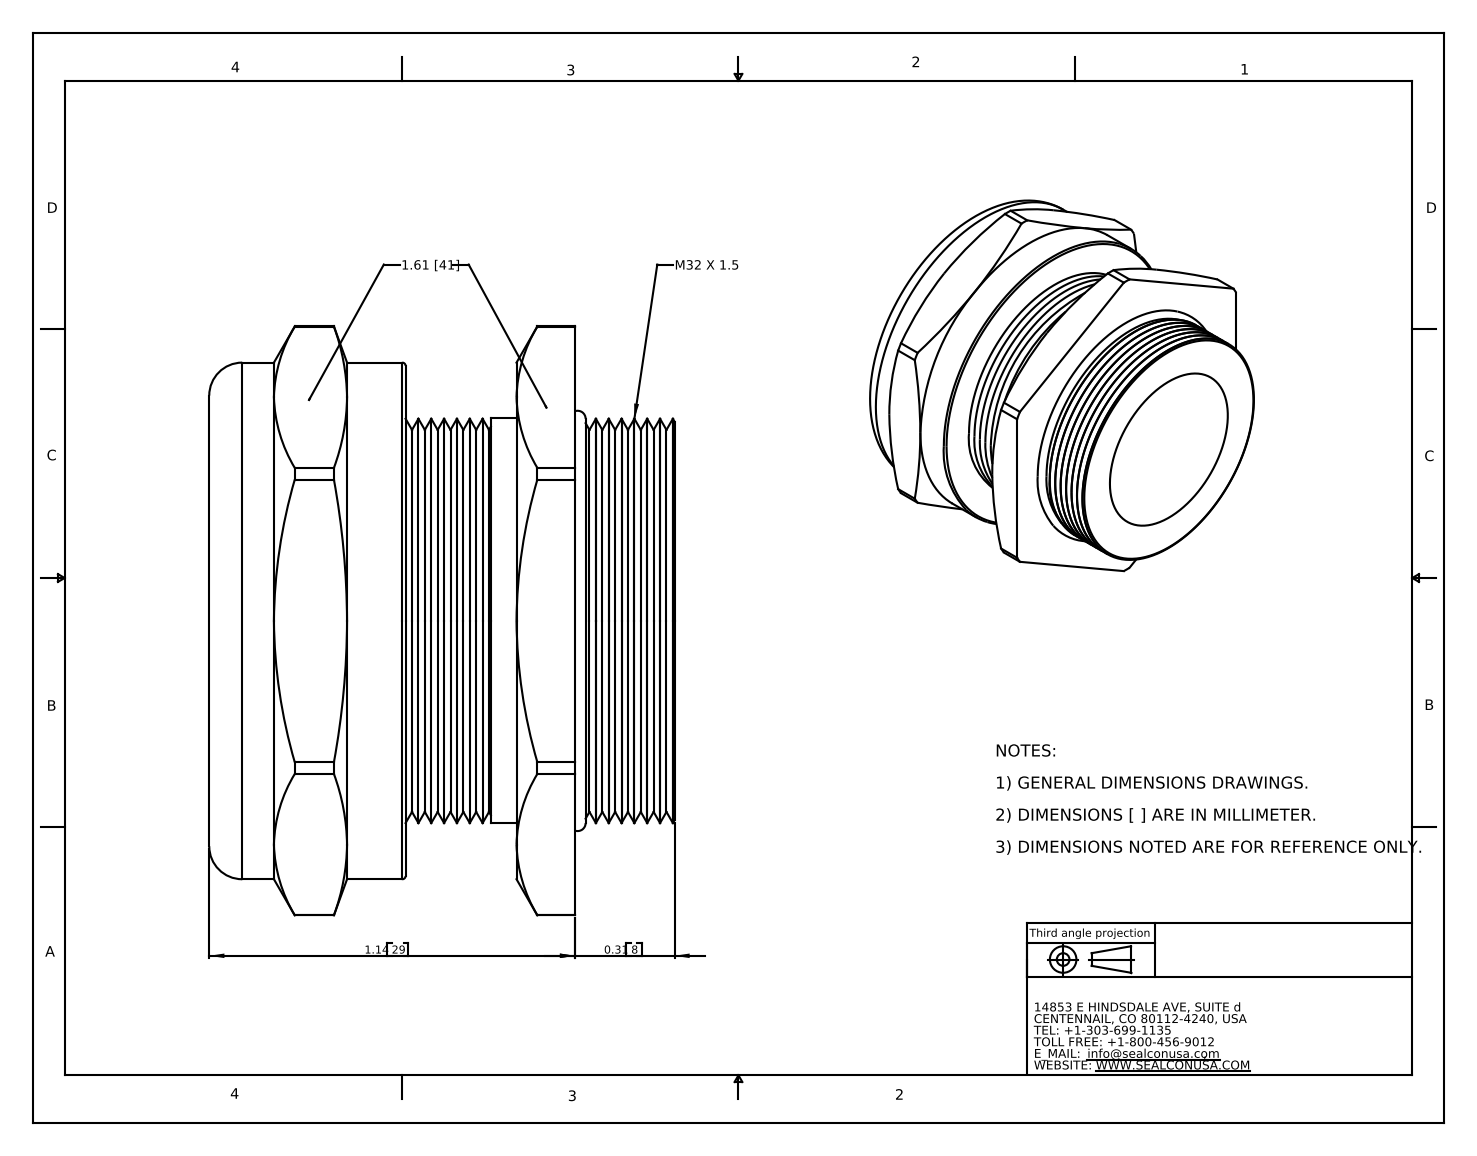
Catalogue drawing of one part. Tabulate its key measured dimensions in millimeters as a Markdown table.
| quantity | value |
| --- | --- |
| part name | CD32MR-SS |
| STEP written by | SolidWorks 2007 (CONFIG_CONTROL_DESIGN) |
| units | millimeters |
| bodies | 2 solids, 152 faces (22 planar, 28 cylindrical, 102 other) |
| overall size | 46.6 × 40.9 × 36.8 |
| volume | 27 940 mm³ |
| surface area | 13 060 mm² |
| round holes (diameter × count) | 20.1 × 1, 29.6 × 1, 32 × 1 |
| round bosses / shafts (diameter × count) | 40.9 × 1, 32.1 × 1 |
| partial cylindrical surfaces (radius × count) | 23.3 × 1 |
| main face-to-face distances | 40.9, 23.9, 19.2, 4.6, 10.4, 8.8, 13.4, 31.7, 21.3, 12.5 |
